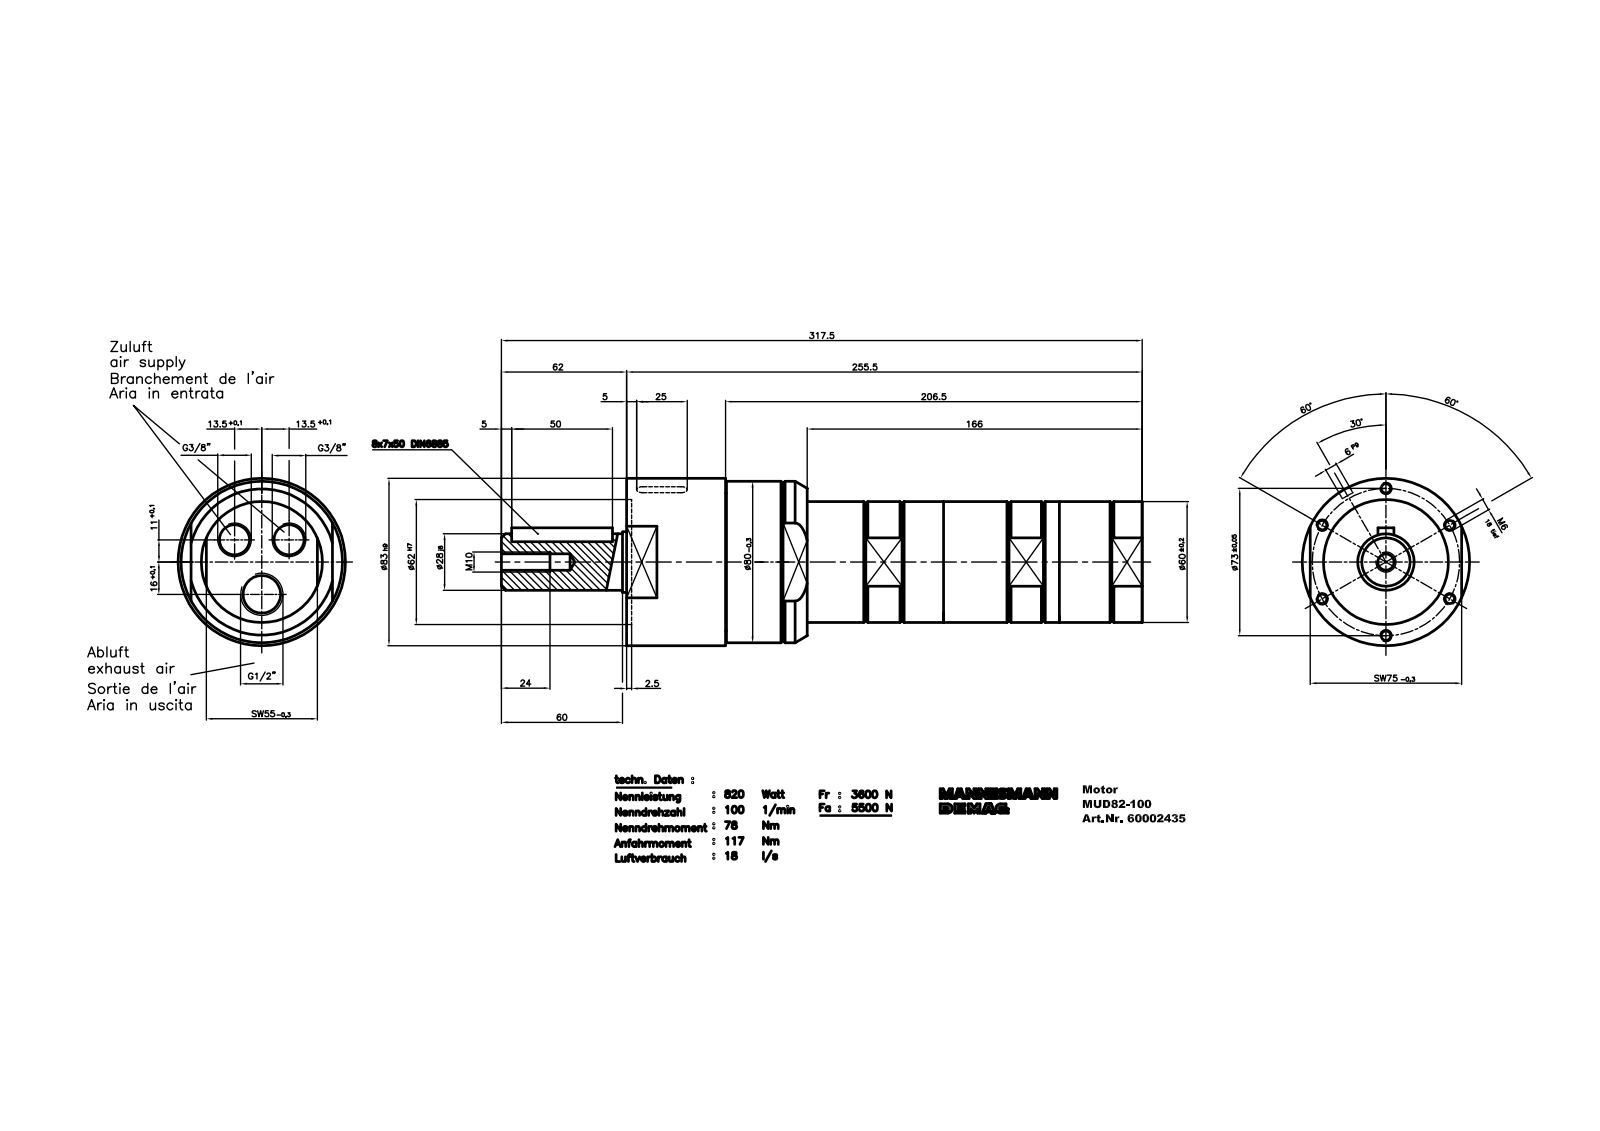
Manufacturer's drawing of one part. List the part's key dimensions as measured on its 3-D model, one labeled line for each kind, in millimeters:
Part name (STEP PRODUCT): MUD 82-100_60002435
STEP written by: Autodesk Inventor 2008 (CONFIG_CONTROL_DESIGN)
Units: millimetres
Bodies: 1 solid, 222 faces (118 planar, 45 cylindrical, 59 other)
Overall size (bounding box): 317.5 × 83 × 83
Volume: 937 922 mm³ · Surface area: 80 934 mm²
Round holes (diameter × count): ⌀5.5 ×2, ⌀1.55 ×1, ⌀38 ×1, ⌀58.69 ×1, ⌀62 ×1
Round bosses / shafts (diameter × count): ⌀5 ×2, ⌀83 ×1, ⌀80 ×1, ⌀75.69 ×1, ⌀60 ×1, ⌀45 ×1, ⌀30 ×1, ⌀28 ×1
Partial cylindrical surfaces — rounded edges, fillets, slot ends (radius × count): R2.25 ×2, R3 ×2, R4 ×2, R7.5 ×2, R8.5 ×1, R23.5 ×1, R30.35 ×1, R32.5 ×1
Main face-to-face distances: 255.5, 89.5, 166, 55, 5, 238.74, 149.24, 16.76, 84.5, 233.74
Hole centre spacings: 1.53
